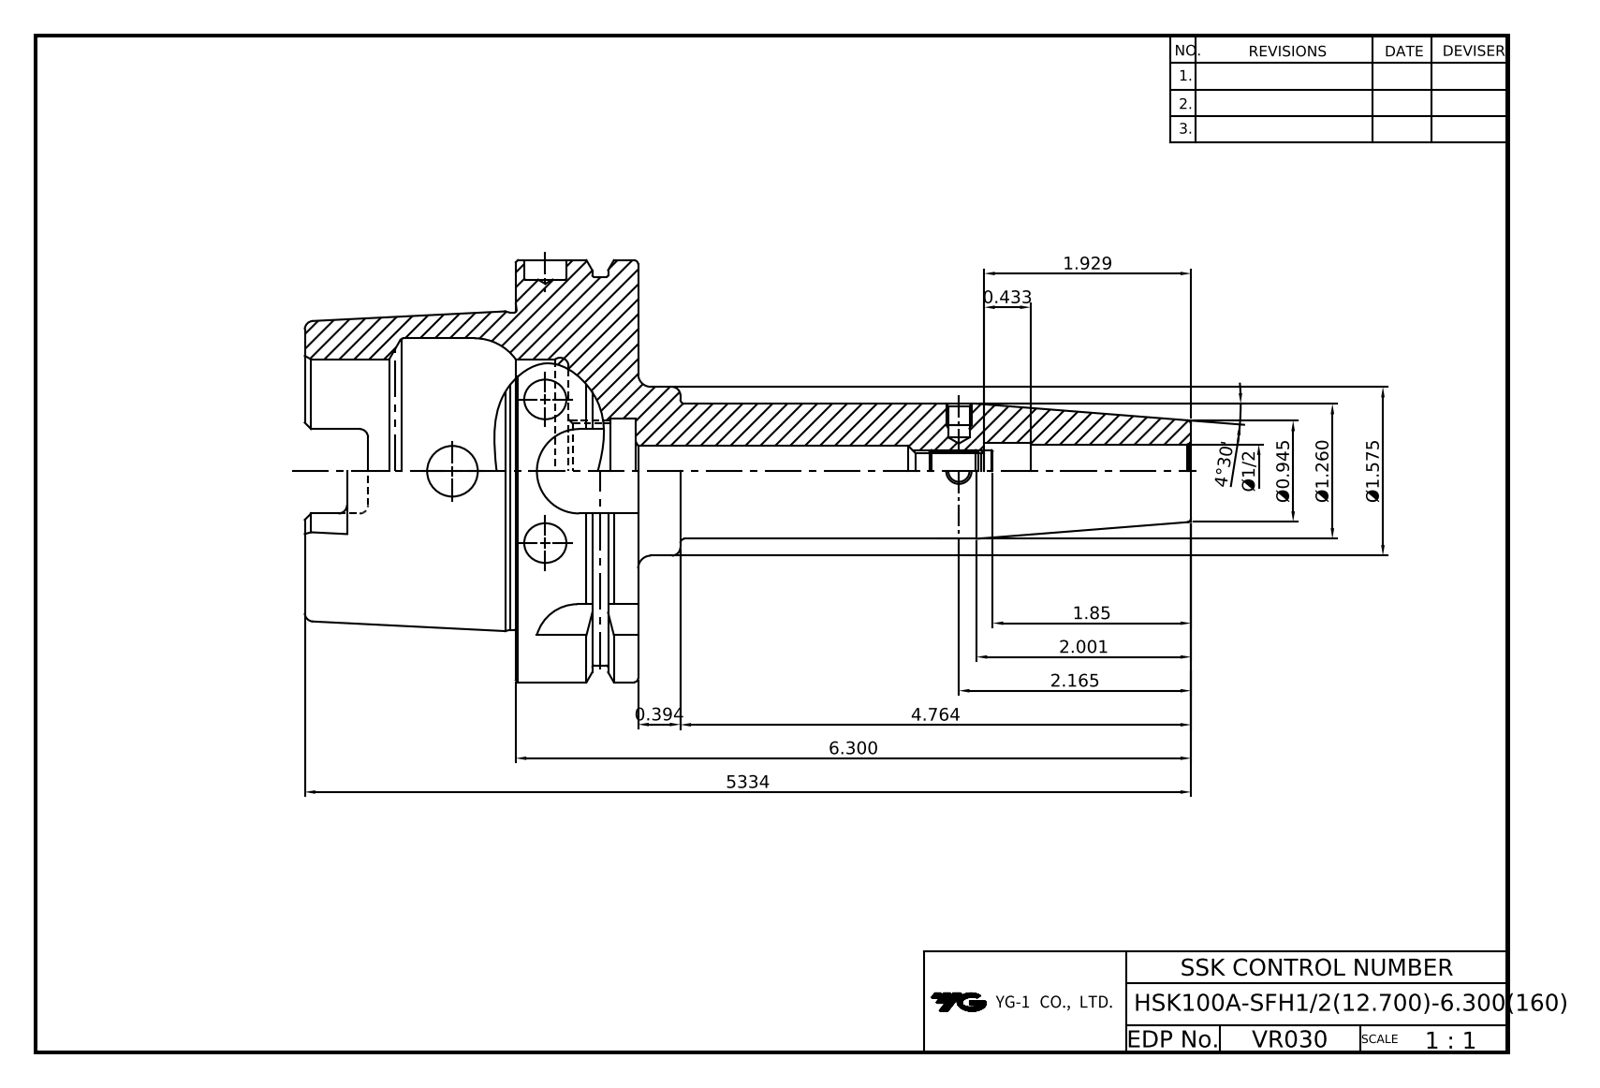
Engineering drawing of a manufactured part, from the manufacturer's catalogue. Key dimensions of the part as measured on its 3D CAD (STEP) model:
Part name (STEP PRODUCT): HSK100A_SFH12_7_160
STEP written by: CREO PARAMETRIC BY PTC INC, 2018400 (CONFIG_CONTROL_DESIGN)
Units: millimetres
Bodies: 1 solid, 206 faces (56 planar, 70 cylindrical, 80 other)
Overall size (bounding box): 210 × 100 × 100
Volume: 336 552 mm³ · Surface area: 68 965 mm²
Round holes (diameter × count): ⌀5 ×2, ⌀6 ×2, ⌀12 ×2, ⌀9 ×1, ⌀10 ×1, ⌀12.7 ×1, ⌀13.3 ×1, ⌀22.5 ×1, ⌀24 ×1, ⌀25 ×1, ⌀53 ×1, ⌀63.96 ×1
Round bosses / shafts (diameter × count): ⌀100 ×1, ⌀92 ×1, ⌀75.16 ×1, ⌀40 ×1, ⌀32 ×1
Partial cylindrical surfaces — rounded edges, fillets, slot ends (radius × count): R2 ×6, R4.88 ×4, R10 ×4
Main face-to-face distances: 29, 16.5, 12.5, 62.5, 79, 10, 50, 72.5, 22.5, 6.5
Hole centre spacings: 98, 120
